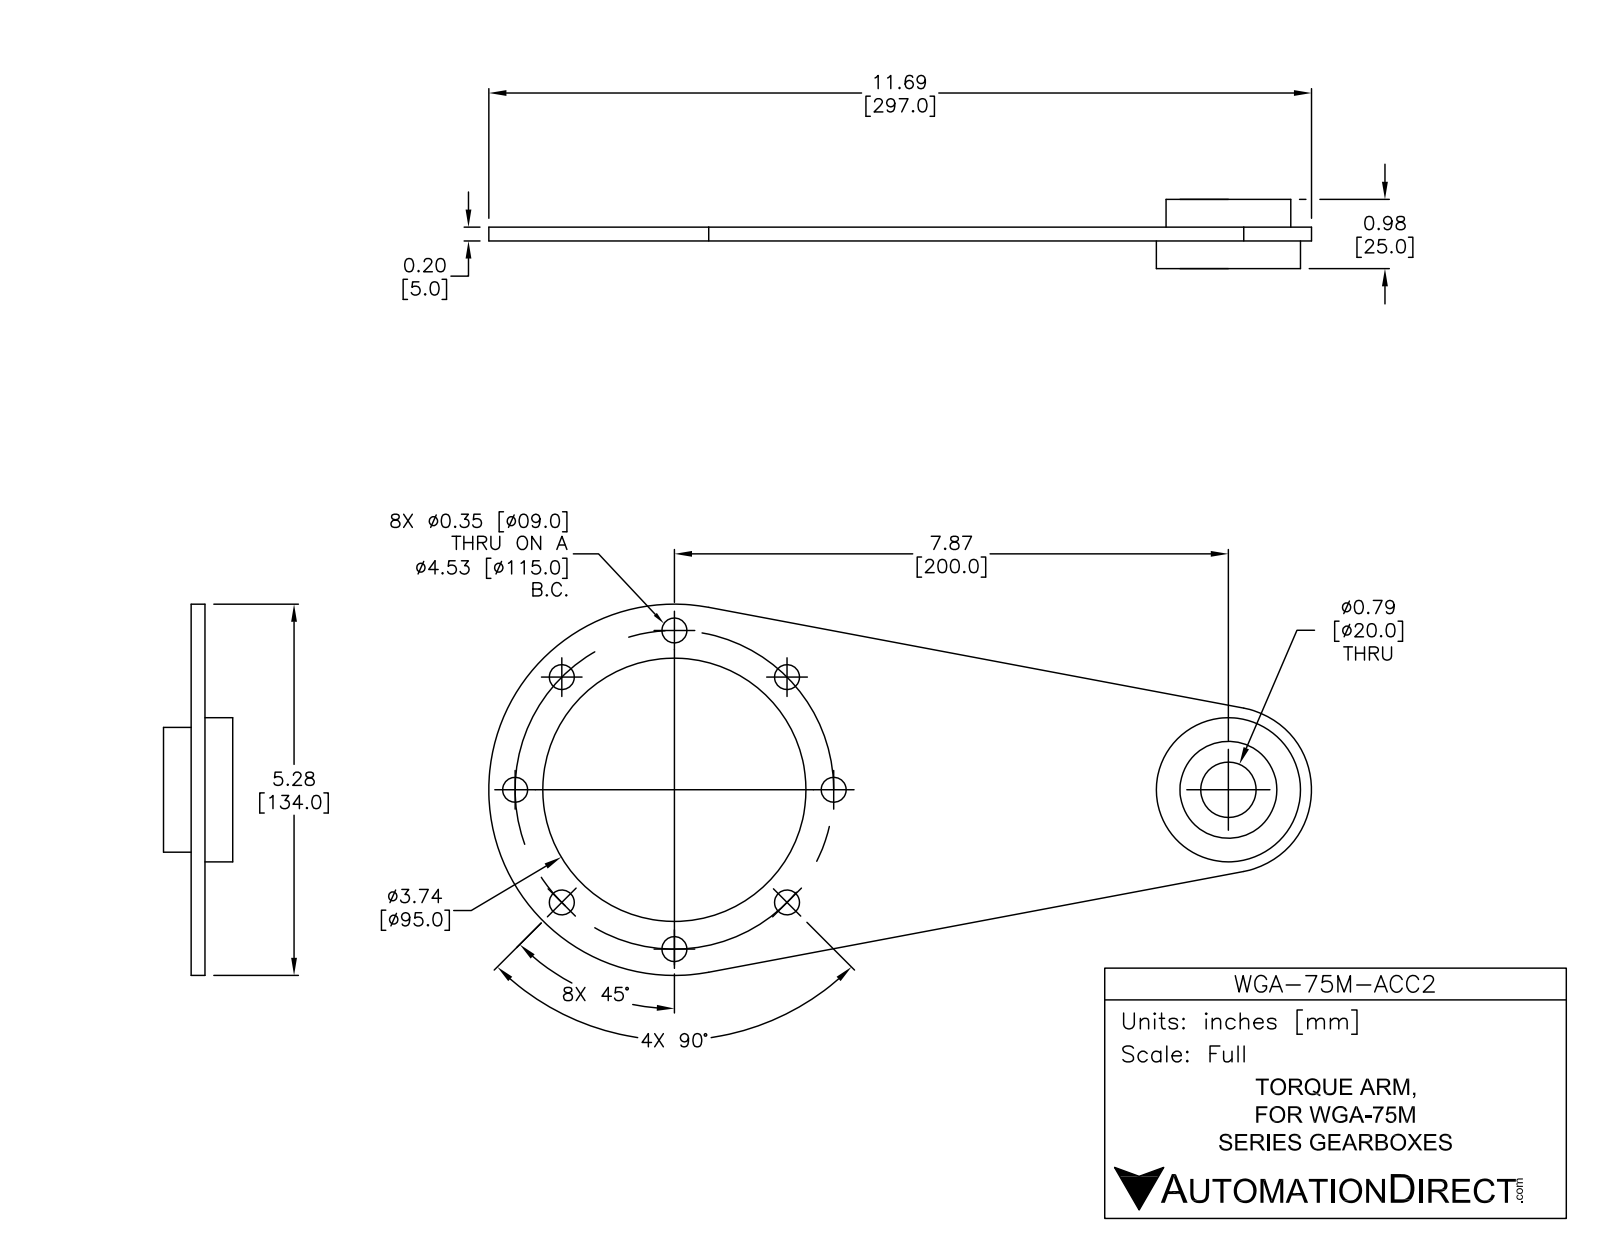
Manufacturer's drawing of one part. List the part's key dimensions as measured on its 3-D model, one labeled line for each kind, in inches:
Part name (STEP PRODUCT): WGA-75M-ACC2
STEP written by: SolidWorks 2014 (AUTOMOTIVE_DESIGN)
Units: inches
Bodies: 2 solids, 40 faces (8 planar, 32 cylindrical, 0 other)
Overall size (bounding box): 11.693 × 5.276 × 0.984
Volume: 8.073 in³ · Surface area: 88.15 in²
Round holes (diameter × count): ⌀0.354 ×8, ⌀0.787 ×1, ⌀1.378 ×1, ⌀3.74 ×1
Round bosses / shafts (diameter × count): ⌀2.047 ×1, ⌀1.772 ×1
Partial cylindrical surfaces — rounded edges, fillets, slot ends (radius × count): R1.181 ×1, R2.638 ×1
Main face-to-face distances: 0.197, 0.394, 0.591, 0.984
Hole centre spacings: 1.733, 2.264, 3.202, 4.183, 4.528, 6.474, 8.193, 9.609
